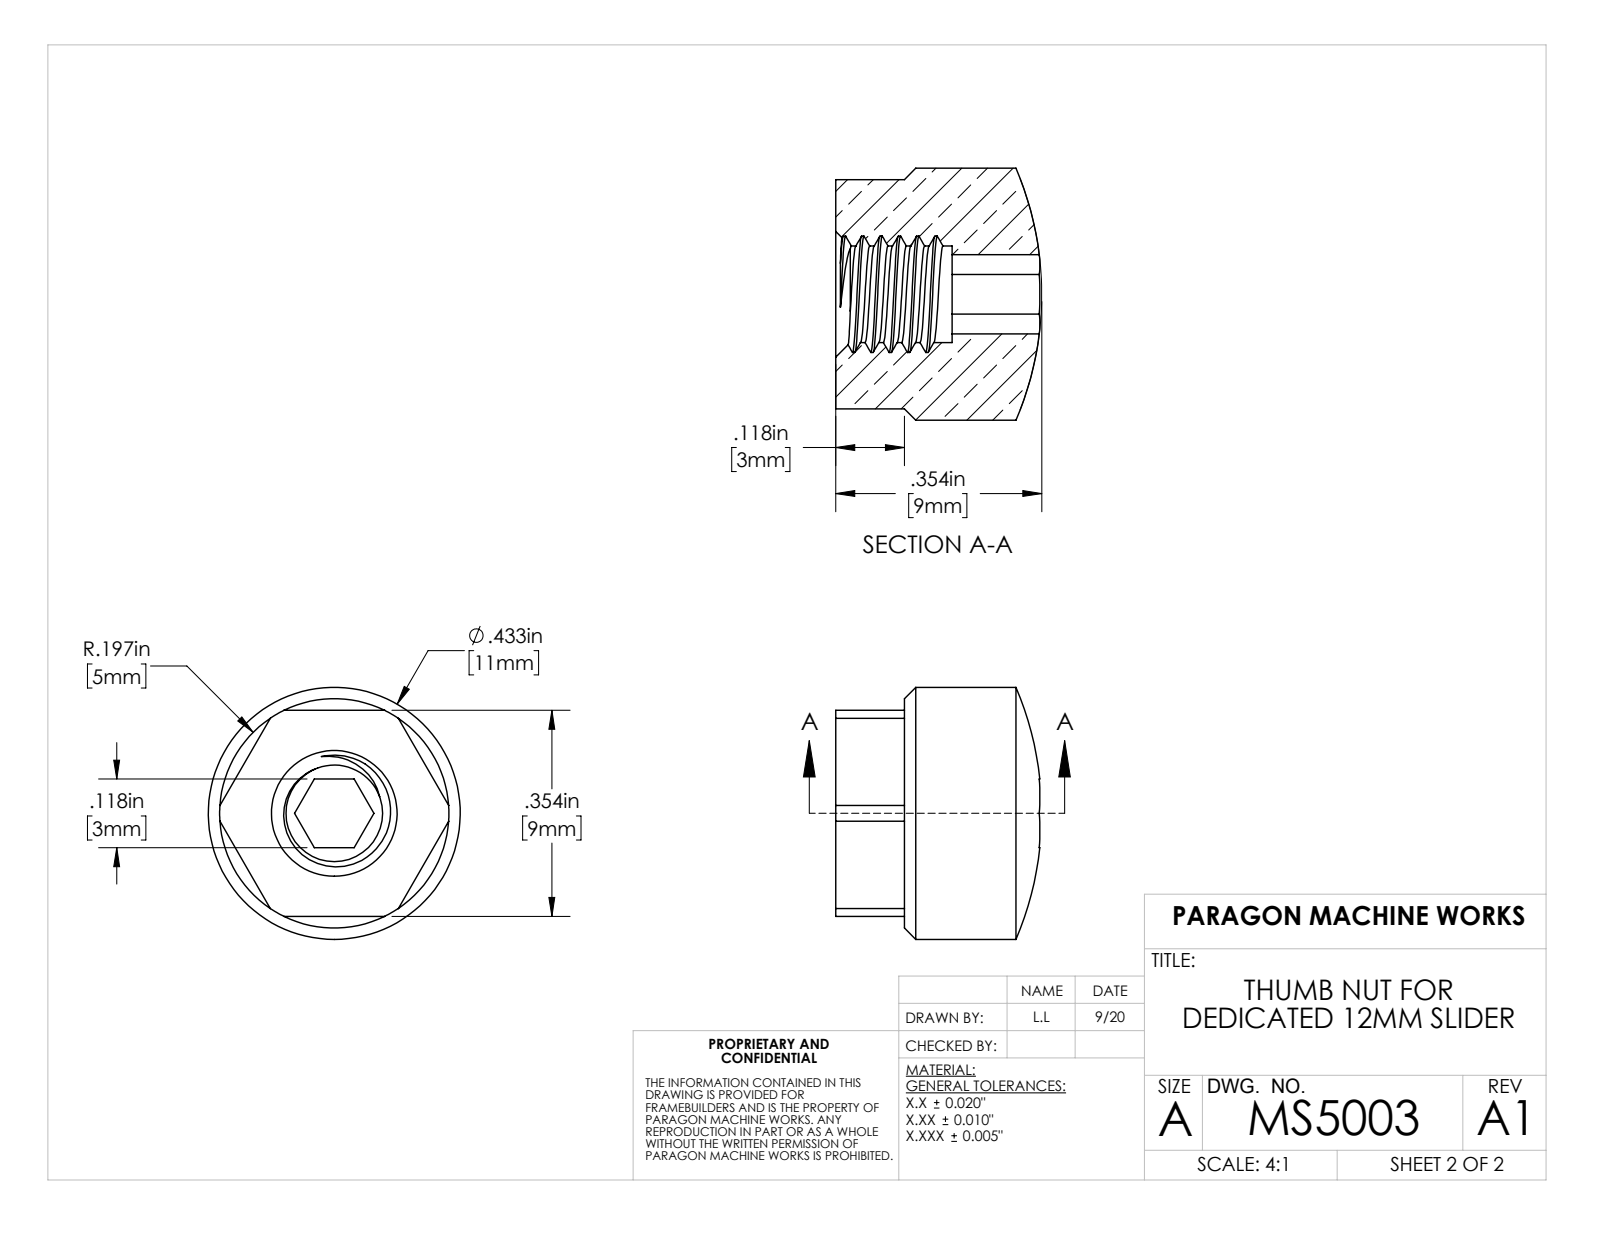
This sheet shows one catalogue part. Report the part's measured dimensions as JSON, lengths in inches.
{"part_name": "MS5003", "step_written_by": "SolidWorks 2020 (AUTOMOTIVE_DESIGN)", "units": "inches", "bodies": {"solids": 1, "faces": 52, "planar": 21, "cylindrical": 21, "other": 10}, "overall_size": [0.433, 0.433, 0.351], "volume_in3": 0.037, "surface_area_in2": 0.89, "round_holes": [[0.166, 1]], "round_bosses_or_shafts": [[0.433, 1]], "partial_cylinders_radius": [[0.197, 1]], "face_to_face_distances": [0.118, 0.236, 0.354, 0.2, 0.082, 0.177, 0.059]}
